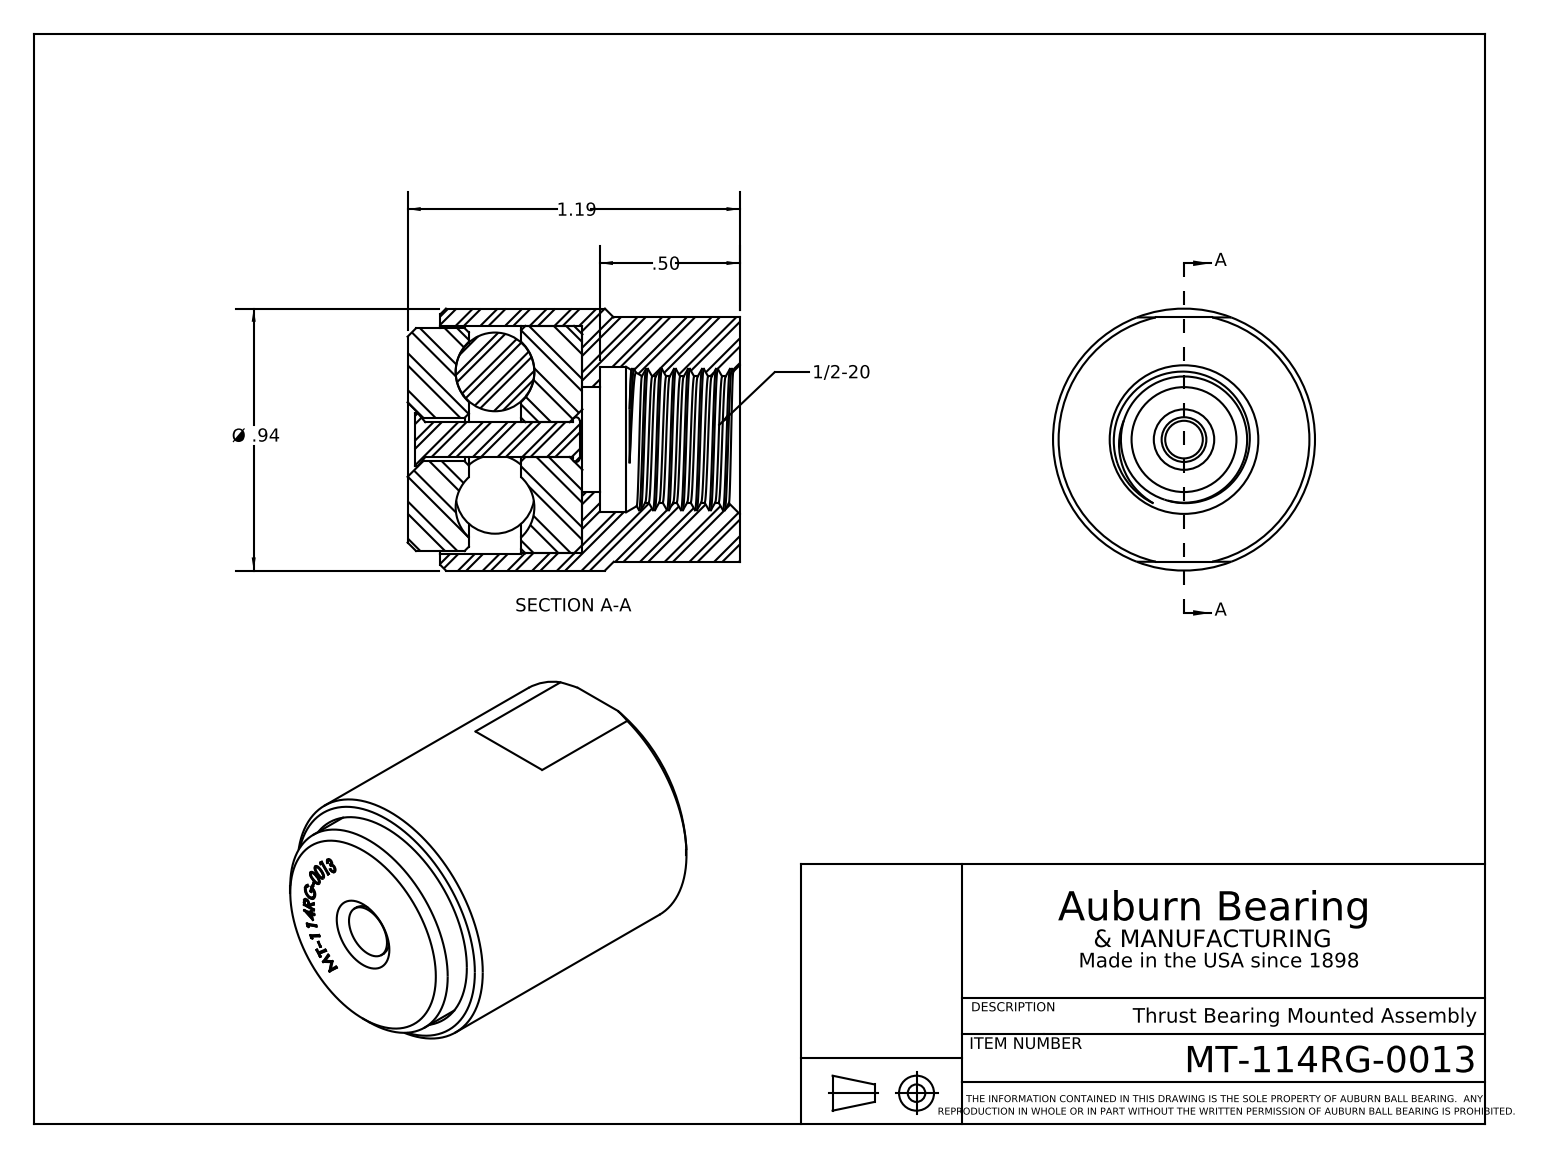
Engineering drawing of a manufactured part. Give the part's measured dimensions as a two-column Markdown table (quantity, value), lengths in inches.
| quantity | value |
| --- | --- |
| part name | MT-114RG-0013 |
| STEP written by | SolidWorks 2020 (CONFIG_CONTROL_DESIGN) |
| units | inches |
| bodies | 9 solids, 244 faces (113 planar, 36 cylindrical, 95 other) |
| overall size | 1.187 × 0.936 × 0.936 |
| volume | 0.621 in³ |
| surface area | 11.44 in² |
| round holes (diameter × count) | 0.125 × 1, 0.156 × 1, 0.375 × 1, 0.451 × 1, 0.52 × 1, 0.811 × 1, 0.816 × 1 |
| round bosses / shafts (diameter × count) | 0.937 × 1, 0.813 × 1, 0.796 × 1, 0.192 × 1 |
| main face-to-face distances | 0.562, 0.625, 1.187, 0.219, 0.406, 0.873, 0.781, 0.117, 0.289, 0.508 |
